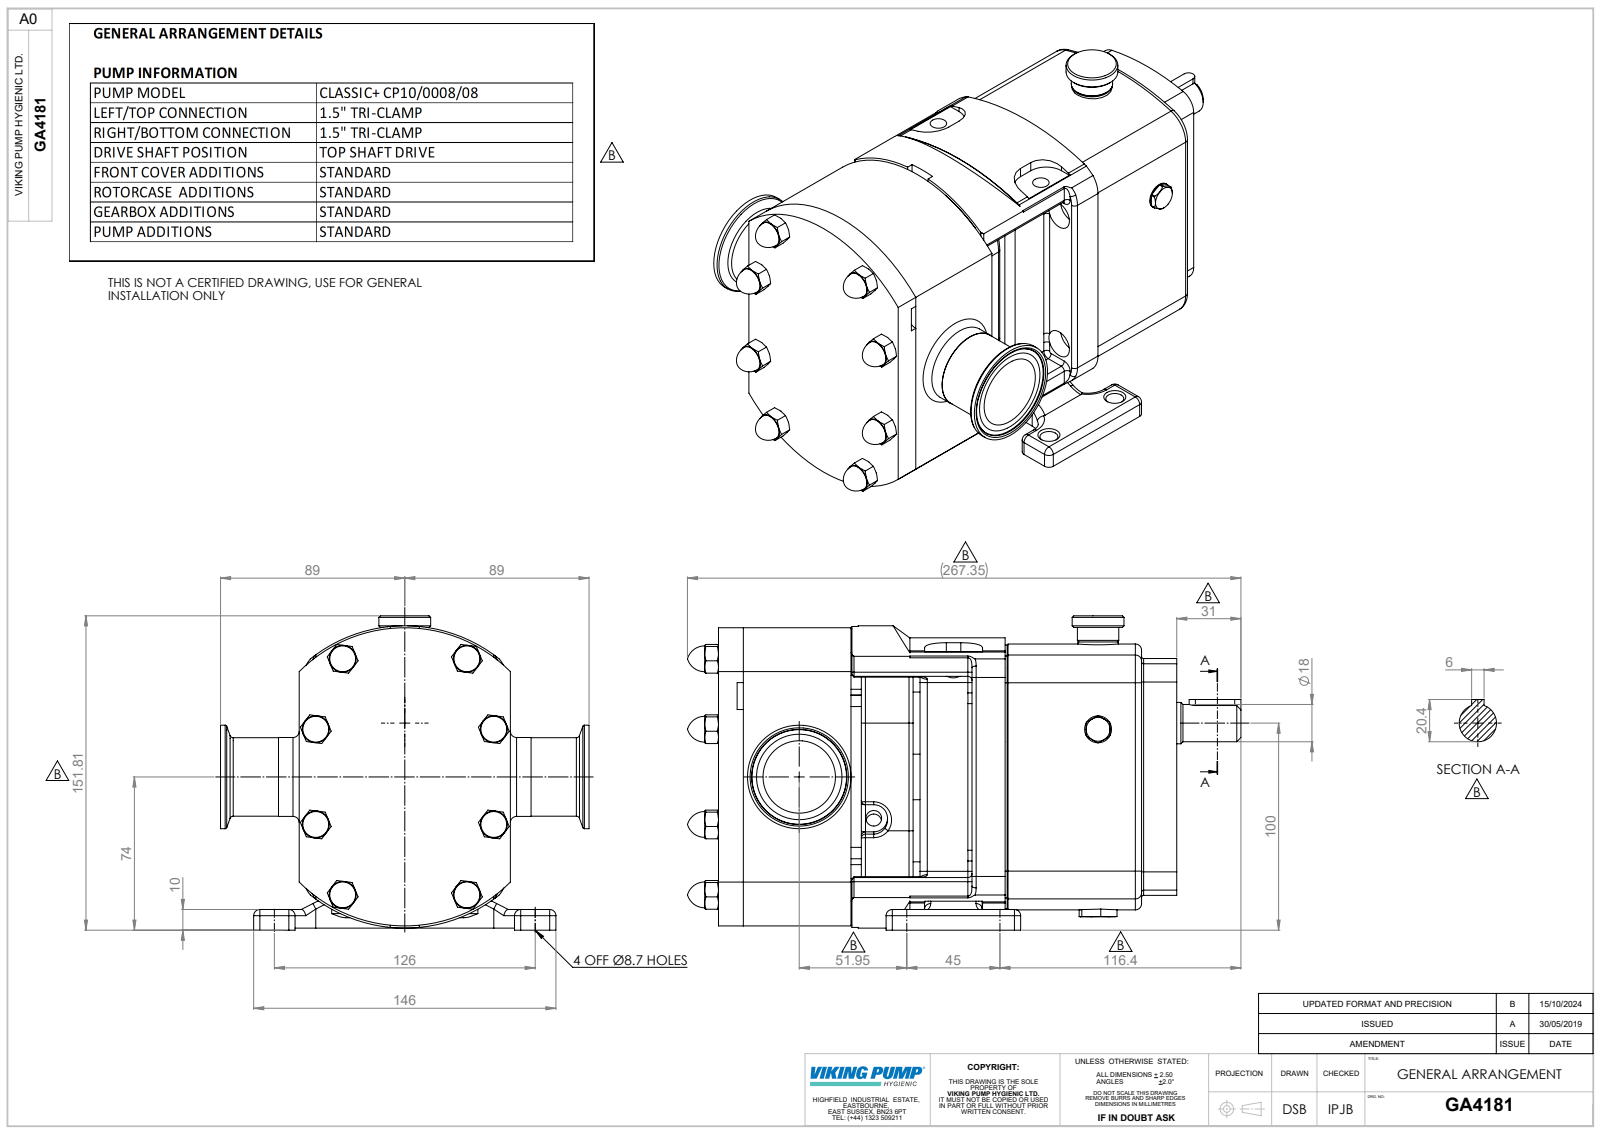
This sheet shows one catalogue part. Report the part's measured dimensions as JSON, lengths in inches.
{"part_name": "GA4181; Copy of Z94-5121-22 - 1.5 INCH^GA4181; Copy of CP10-0008-08 H T^GA4181", "step_written_by": "SolidWorks 2023 (AUTOMOTIVE_DESIGN)", "units": "inches", "bodies": {"solids": 3, "faces": 764, "planar": 254, "cylindrical": 218, "other": 292}, "overall_size": [10.526, 7.008, 5.977], "volume_in3": 150.4, "surface_area_in2": 297.7, "round_holes": [[0.343, 4], [0.551, 4], [0.3, 2], [0.315, 2], [0.887, 1], [1.378, 1]], "round_bosses_or_shafts": [[1.181, 2], [1.969, 1], [1.5, 1], [1.492, 1], [0.985, 1], [0.787, 1], [0.787, 1], [0.768, 1]], "partial_cylinders_radius": [[0.079, 30], [0.118, 26], [0.531, 12], [0.413, 8], [0.138, 6], [0.217, 4], [0.236, 4], [0.354, 4]], "face_to_face_distances": [0.197, 8.715, 4.882, 4.016, 3.819, 0.197, 3.622, 3.819, 3.833, 0.827], "hole_center_spacings": [1.414, 3.959, 1.772, 2.992, 3.032, 4.26, 4.961, 5.267]}
